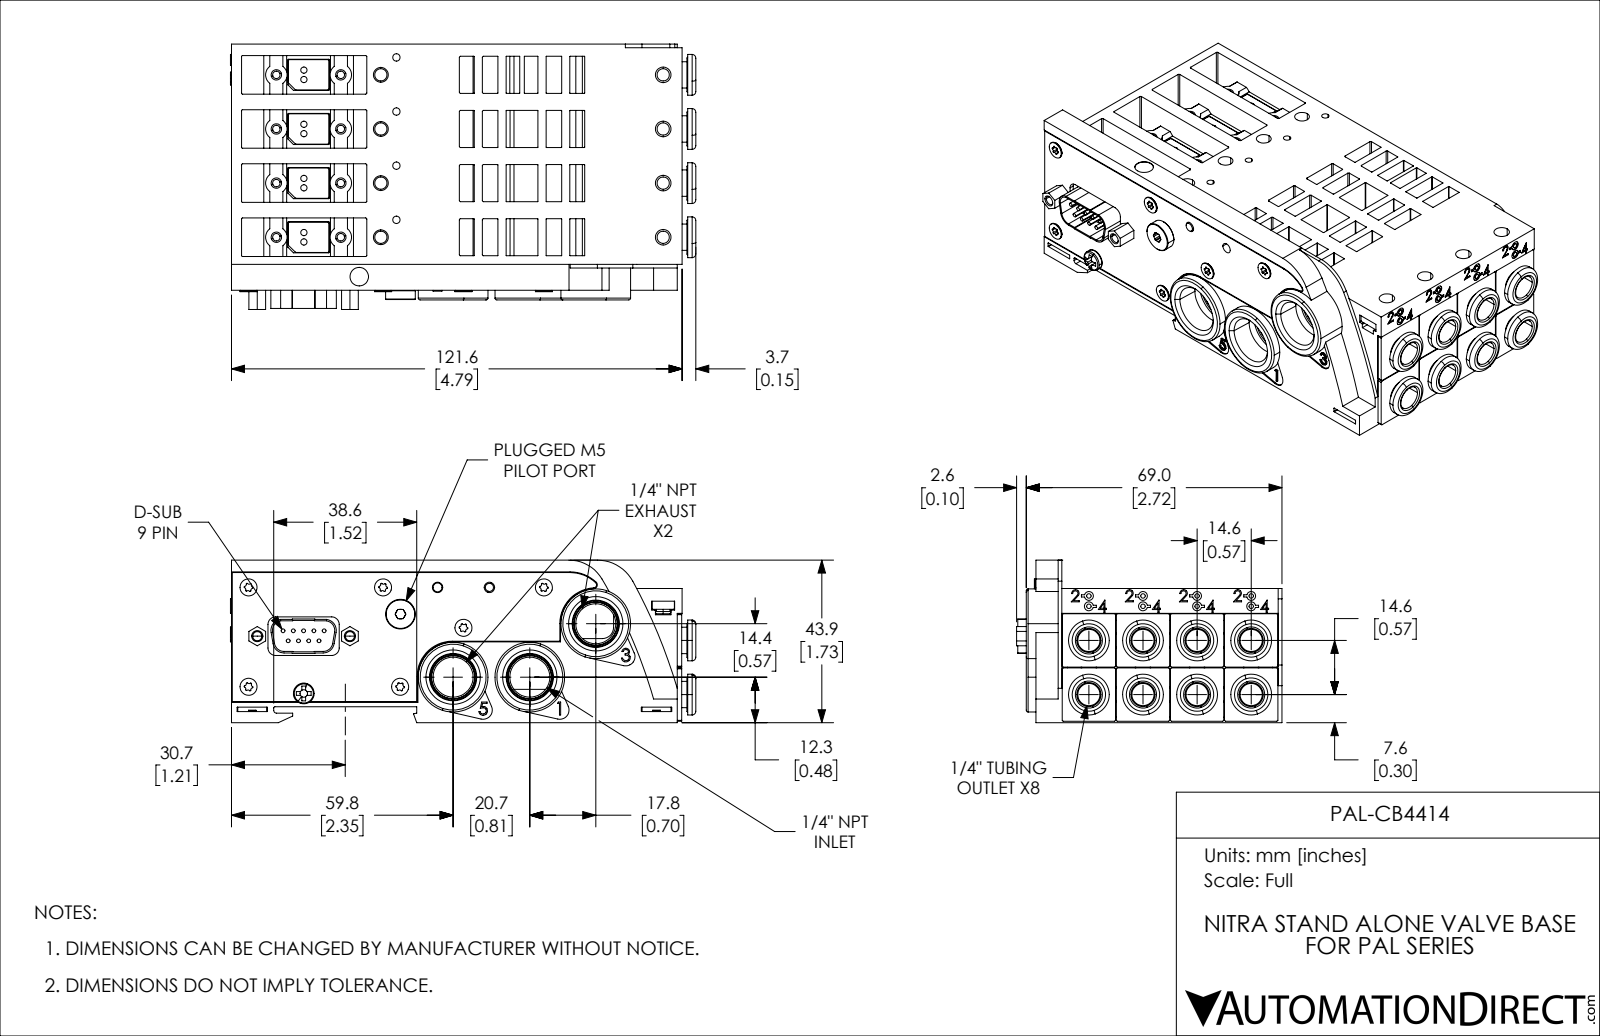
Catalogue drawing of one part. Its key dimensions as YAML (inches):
part_name: "PAL-CB4414"
step_written_by: "SolidWorks 2019 (CONFIG_CONTROL_DESIGN)"
units: inches
bodies: {solids: 9, faces: 2468, planar: 1216, cylindrical: 1036, other: 216}
overall_size: [4.945, 2.819, 1.727]
volume: 13.94
surface_area: 126.7
round_holes:
  - {diameter: 0.079, count: 12}
  - {diameter: 0.524, count: 11}
  - {diameter: 0.197, count: 9}
  - {diameter: 0.236, count: 9}
  - {diameter: 0.067, count: 8}
  - {diameter: 0.094, count: 8}
  - {diameter: 0.13, count: 8}
  - {diameter: 0.256, count: 8}
  - {diameter: 0.157, count: 6}
  - {diameter: 0.165, count: 4}
  - {diameter: 0.425, count: 3}
  - {diameter: 0.457, count: 3}
round_bosses_or_shafts:
  - {diameter: 0.04, count: 9}
  - {diameter: 0.516, count: 8}
  - {diameter: 0.453, count: 8}
  - {diameter: 0.433, count: 8}
  - {diameter: 0.429, count: 8}
  - {diameter: 0.374, count: 8}
  - {diameter: 0.354, count: 8}
  - {diameter: 0.335, count: 8}
partial_cylinders:
  - {radius: 0.012, count: 110}
  - {radius: 0.004, count: 73}
  - {radius: 0.007, count: 36}
  - {radius: 0.023, count: 36}
  - {radius: 0.008, count: 34}
  - {radius: 0.01, count: 22}
  - {radius: 0.079, count: 12}
  - {radius: 0.114, count: 8}
face_to_face_distances: [1.425, 0.575, 0.252, 0.169, 1.256, 2.614, 0.087, 0.165, 1.15, 0.677]
hole_center_spacings: [0.575, 1.15, 1.724, 0.819, 0.297, 0.396, 3.818, 0.585]
